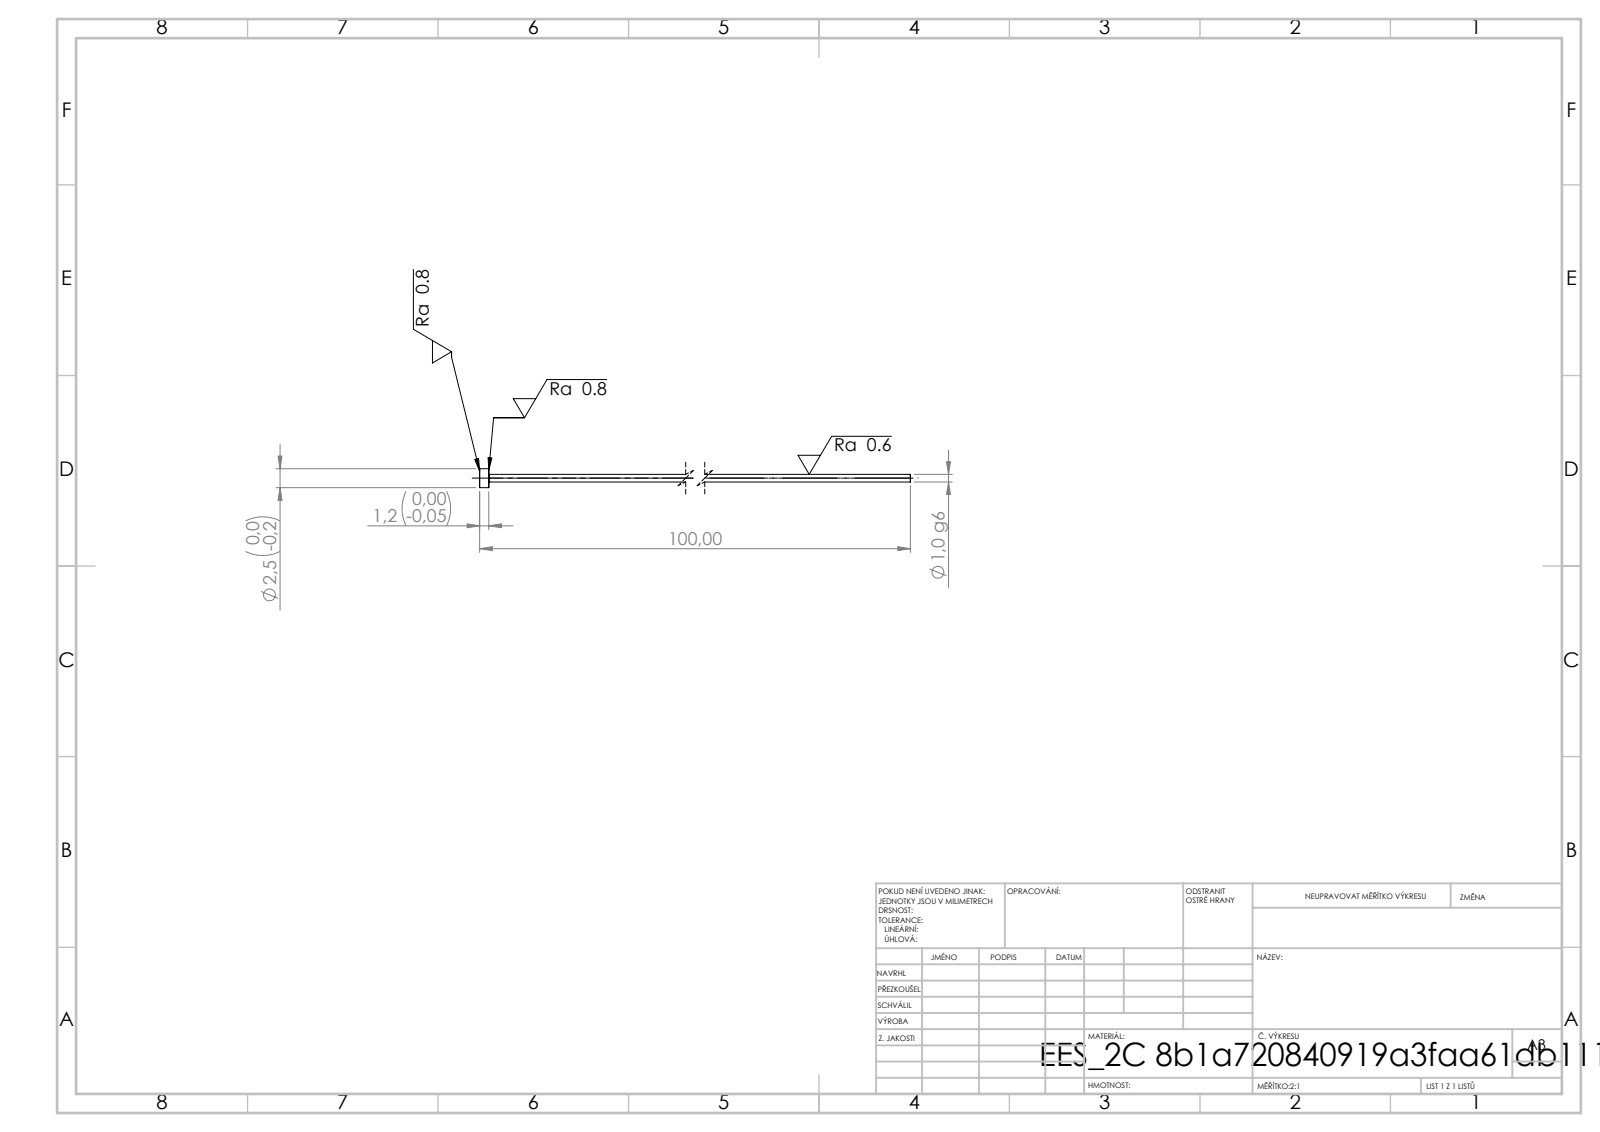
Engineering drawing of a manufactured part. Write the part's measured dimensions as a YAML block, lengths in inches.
step_written_by: "SolidWorks 2019 (CONFIG_CONTROL_DESIGN)"
units: inches
bodies: {solids: 1, faces: 7, planar: 3, cylindrical: 4, other: 0}
overall_size: [3.937, 0.098, 0.098]
volume: 0.005
surface_area: 0.512
round_bosses_or_shafts:
  - {diameter: 0.098, count: 1}
  - {diameter: 0.039, count: 1}
face_to_face_distances: [0.047, 3.937, 3.89]
